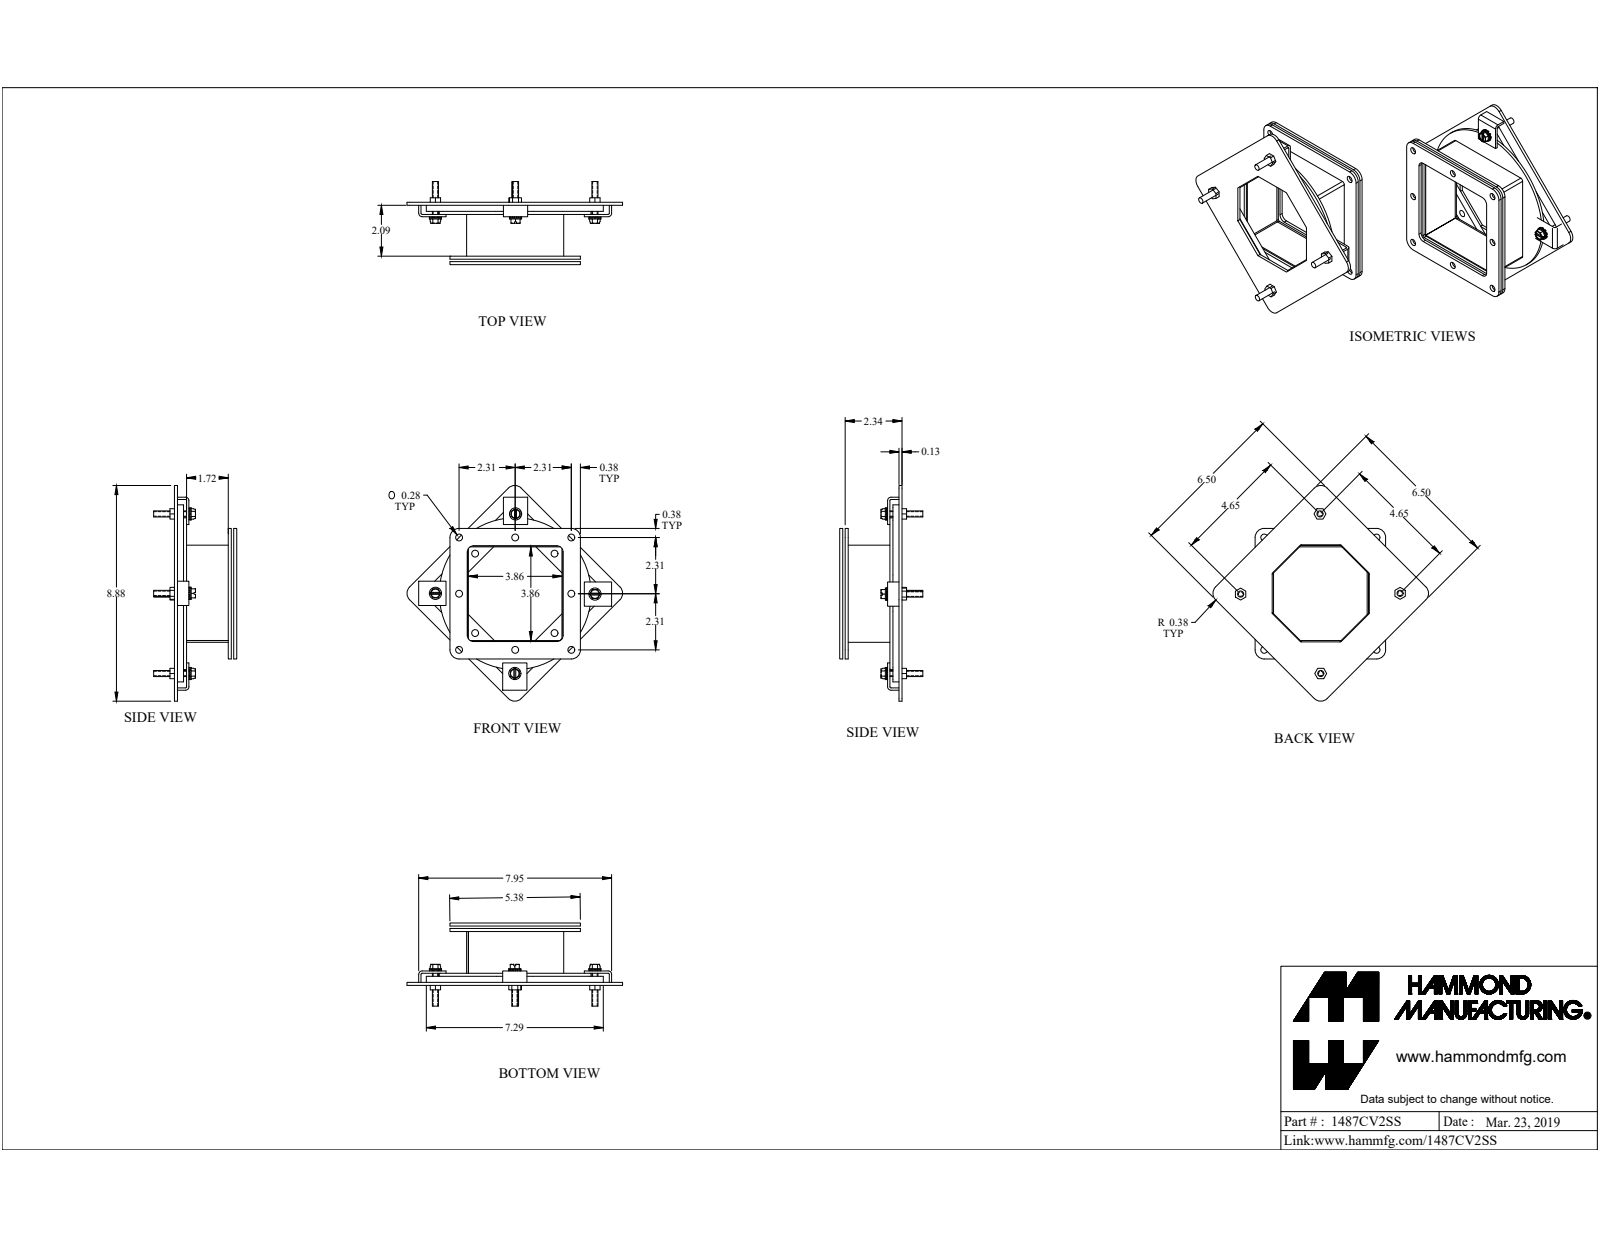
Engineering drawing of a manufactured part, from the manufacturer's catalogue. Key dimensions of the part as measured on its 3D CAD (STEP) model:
Part name (STEP PRODUCT): 1487CV2SS
STEP written by: SolidWorks 2019 (CONFIG_CONTROL_DESIGN)
Units: inches
Bodies: 25 solids, 604 faces (379 planar, 185 cylindrical, 40 other)
Overall size (bounding box): 8.882 × 8.882 × 3.769
Volume: 14.91 in³ · Surface area: 278.2 in²
Round holes (diameter × count): ⌀0.281 ×16, ⌀0.196 ×5, ⌀0.258 ×5, ⌀0.35 ×5, ⌀0.312 ×4, ⌀0.375 ×4
Round bosses / shafts (diameter × count): ⌀0.5 ×5, ⌀0.25 ×5, ⌀6.25 ×1
Partial cylindrical surfaces — rounded edges, fillets, slot ends (radius × count): R0.02 ×30, R0.375 ×12, R0.25 ×8, R0.048 ×4, R0.062 ×4, R0.062 ×4, R0.143 ×4, R0.036 ×3
Main face-to-face distances: 0.125, 0.125, 0.25, 0.375, 1.843, 0.072, 3.928, 2.443, 0.5, 0.375
Hole centre spacings: 2.313, 4.625, 3.27, 5.171, 5.171, 0.973, 2.495, 2.523
